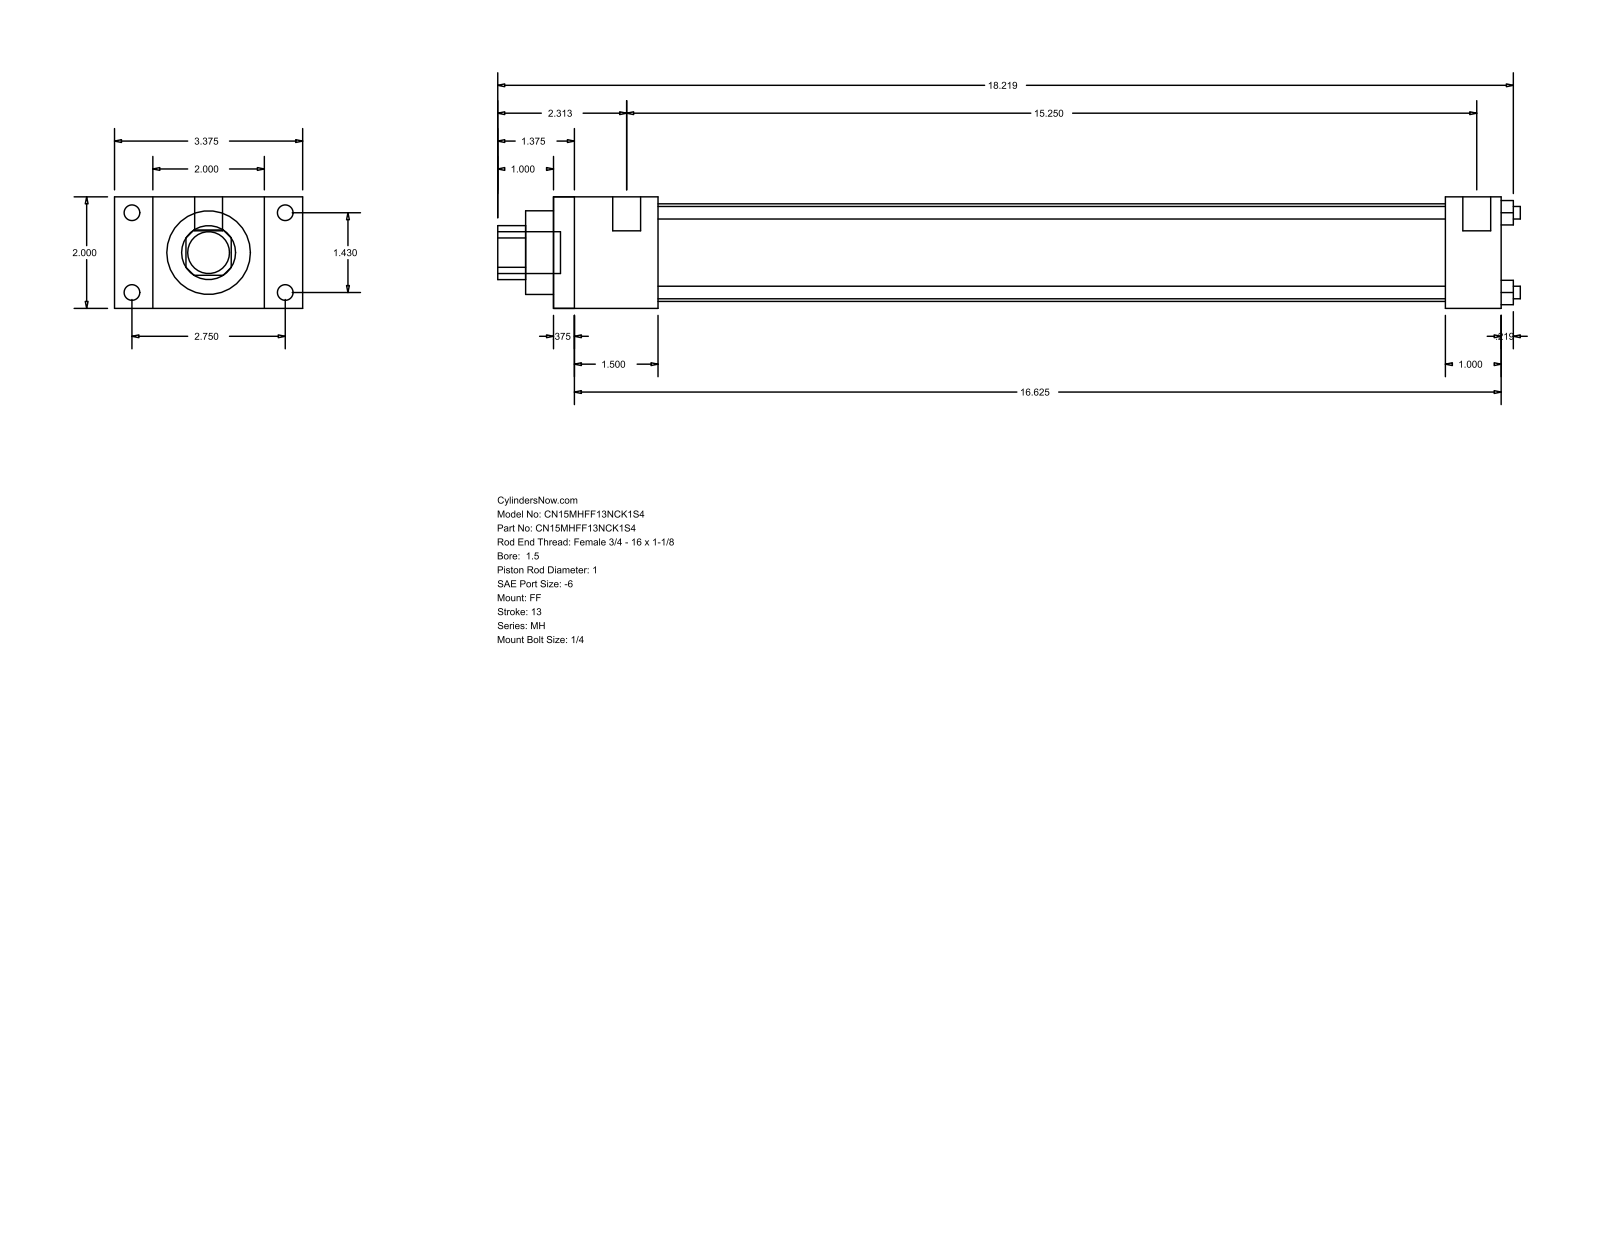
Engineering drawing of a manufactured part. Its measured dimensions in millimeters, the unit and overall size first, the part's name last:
Units: millimetres
Overall size (bounding box): 465.93 × 85.72 × 50.8
Round holes (diameter × count): ⌀5.71 ×4, ⌀25.4 ×1, ⌀38.1 ×1, ⌀44.45 ×1
Round bosses / shafts (diameter × count): ⌀7.14 ×4, ⌀5.56 ×4, ⌀12.7 ×2, ⌀19.05 ×1
Partial cylindrical surfaces — rounded edges, fillets, slot ends (radius × count): R12.29 ×1
Main face-to-face distances: 50.8, 431.8, 9.52, 422.28, 25.4, 17.46, 68.26, 47.63, 38.11, 384.17
Hole centre spacings: 25.68, 36.32, 51.36
Bodies: 0 solids, 92 faces (64 planar, 28 cylindrical, 0 other)
Part name (STEP PRODUCT): MH_FF__0150_1
STEP written by: GSSL Pune (CONFIG_CONTROL_DESIGN)
